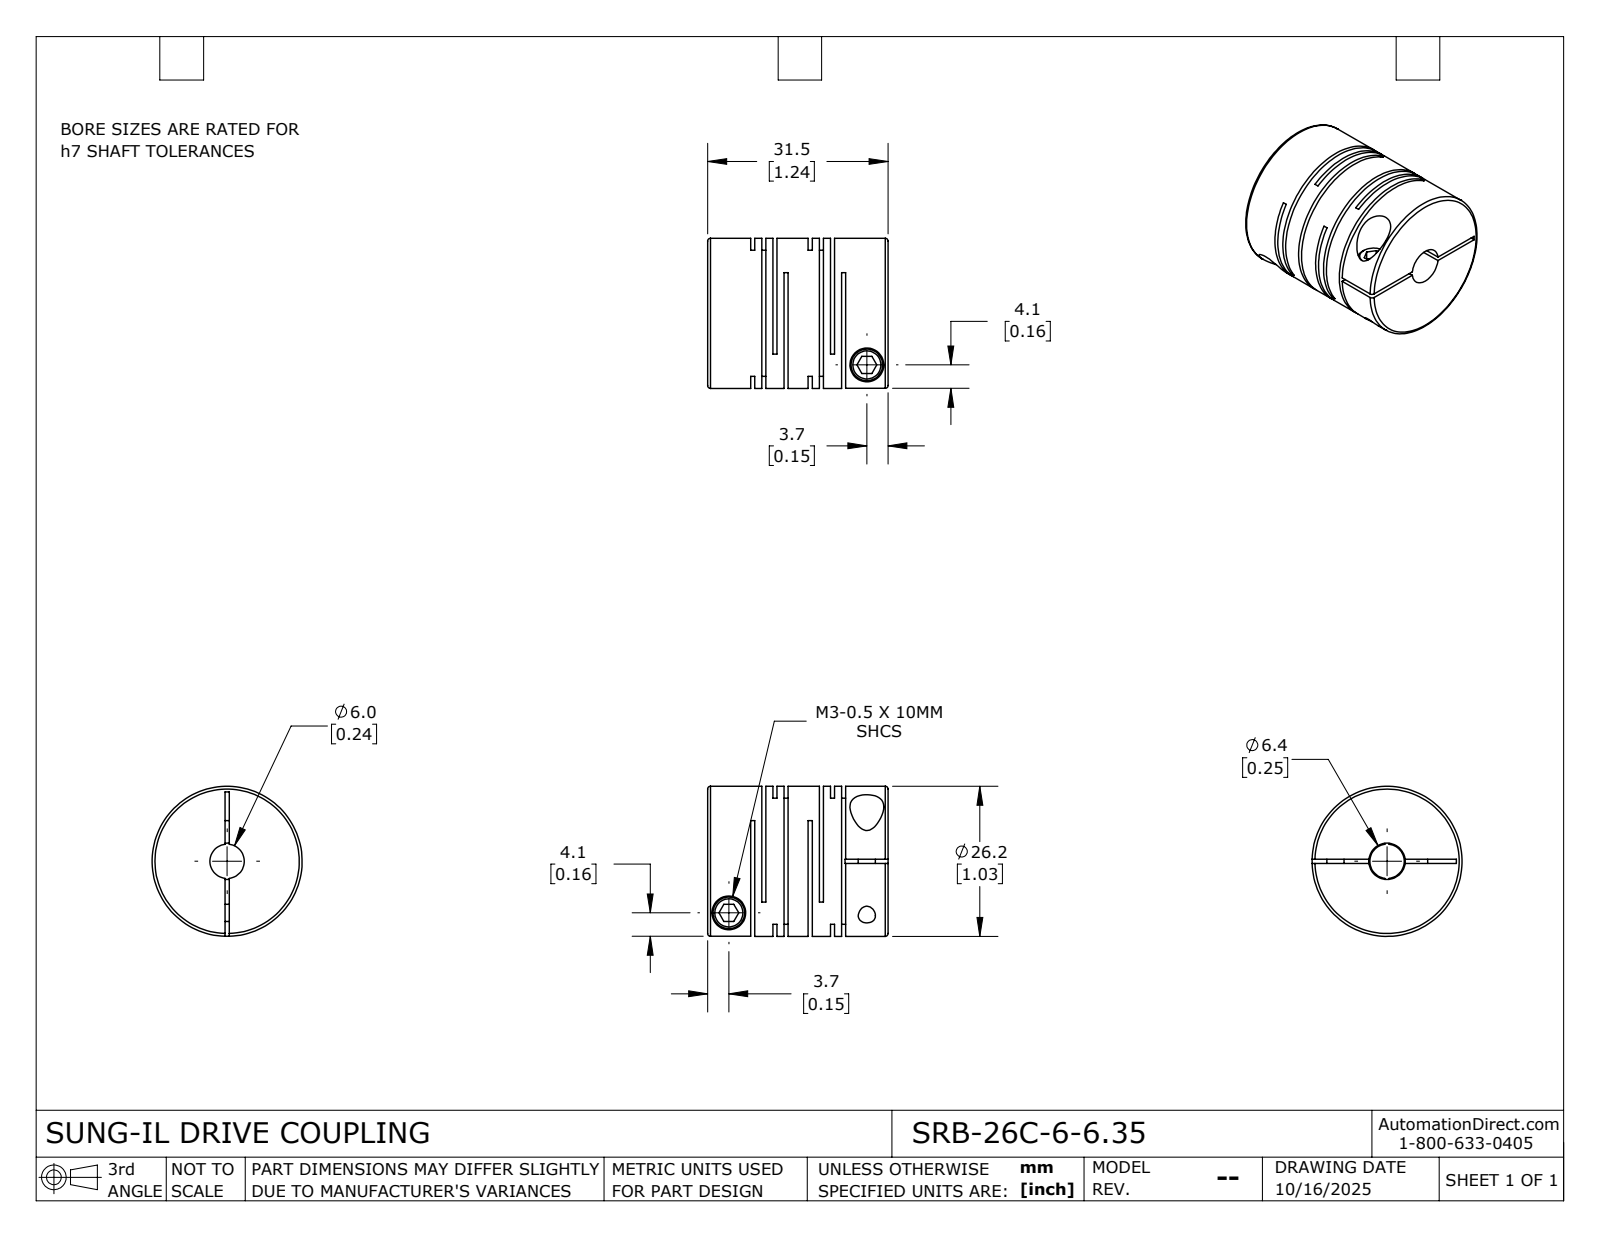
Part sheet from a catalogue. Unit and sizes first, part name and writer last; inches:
Units: inches
Overall size (bounding box): 1.24 × 1.031 × 1.031
Round holes (diameter × count): ⌀0.118 ×2, ⌀0.232 ×2, ⌀0.236 ×1, ⌀0.25 ×1
Round bosses / shafts (diameter × count): ⌀0.217 ×2, ⌀1.031 ×1
Main face-to-face distances: 0.077, 0.396, 0.028, 0.154, 0.319, 0.472, 0.049, 0.105, 0.368, 0.549
Volume: 0.802 in³ · Surface area: 17.63 in²
Bodies: 1 solid, 115 faces (60 planar, 42 cylindrical, 13 other)
Part name (STEP PRODUCT): SRB-26C-6-6.35
STEP written by: SolidWorks 2024 (CONFIG_CONTROL_DESIGN)
